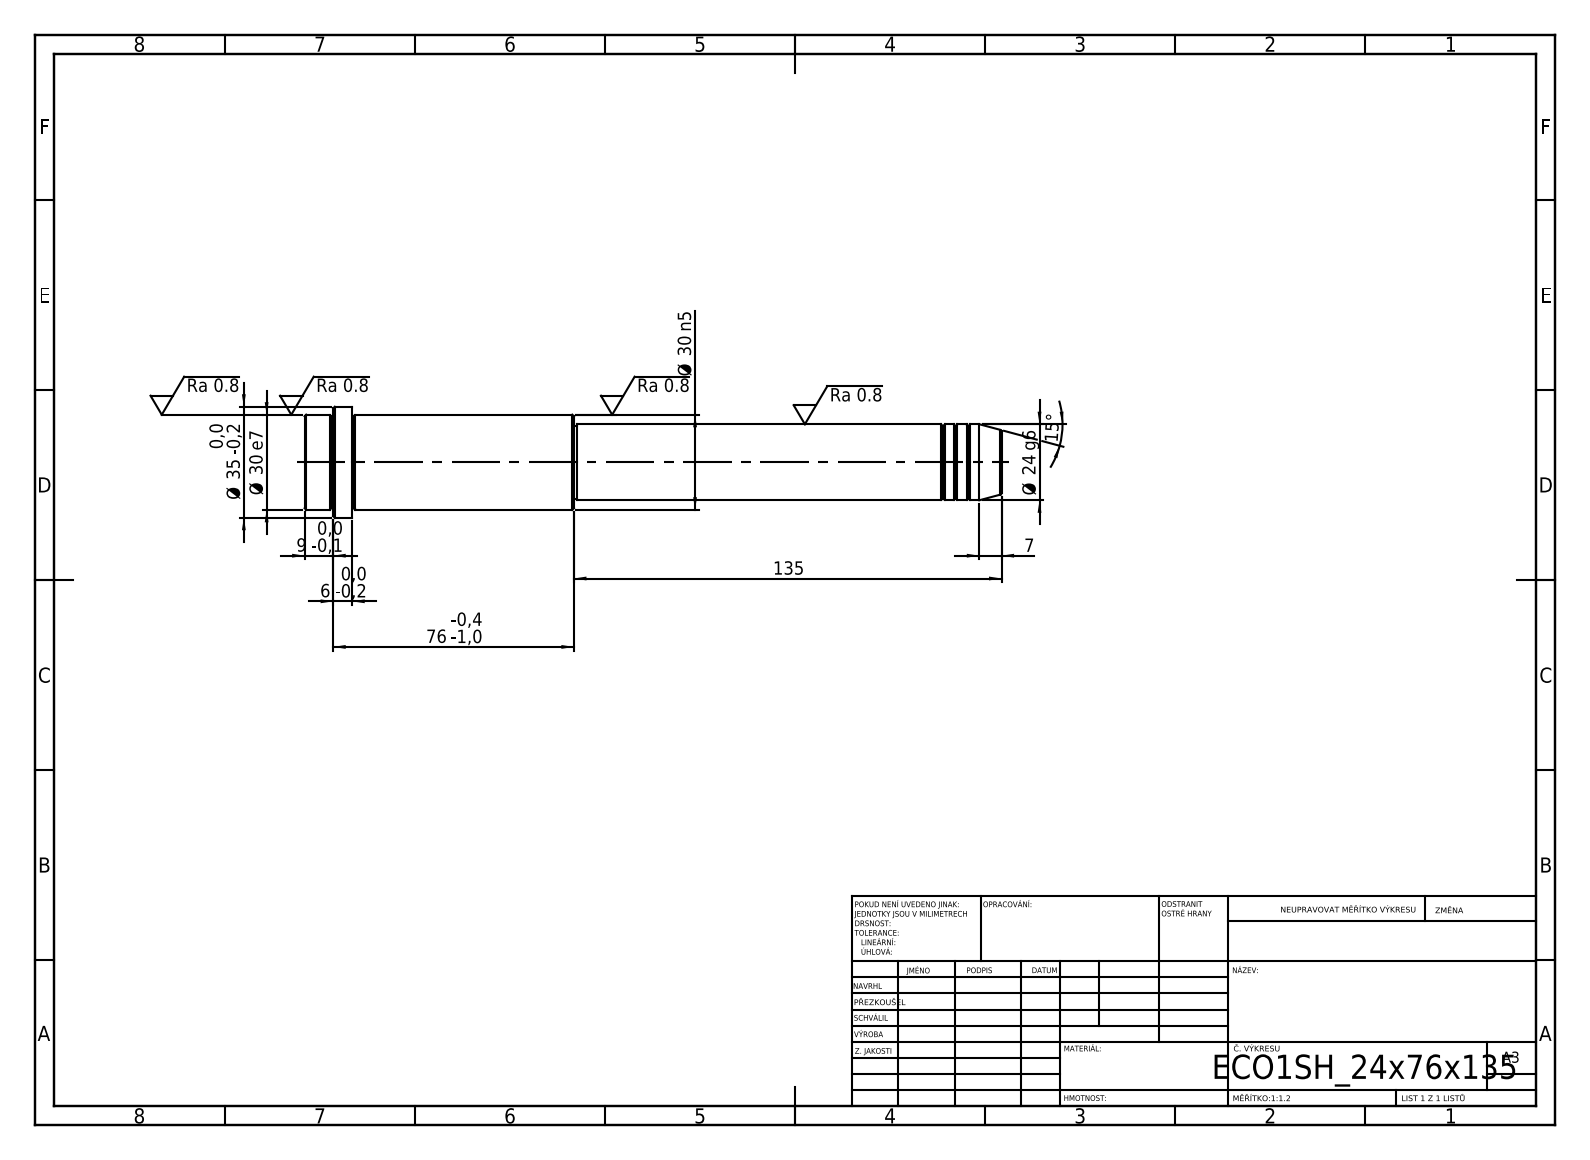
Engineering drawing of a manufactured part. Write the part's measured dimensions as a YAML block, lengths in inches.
step_written_by: "SolidWorks 2019 (CONFIG_CONTROL_DESIGN)"
units: inches
bodies: {solids: 1, faces: 52, planar: 6, cylindrical: 16, other: 30}
overall_size: [8.661, 1.378, 1.378]
volume: 7.444
surface_area: 31.39
round_bosses_or_shafts:
  - {diameter: 1.378, count: 1}
  - {diameter: 1.181, count: 1}
  - {diameter: 0.945, count: 1}
  - {diameter: 0.906, count: 1}
face_to_face_distances: [8.661, 8.071, 0.591, 5.315, 2.756, 3.346, 8.307, 2.992, 0.236, 0.354]
